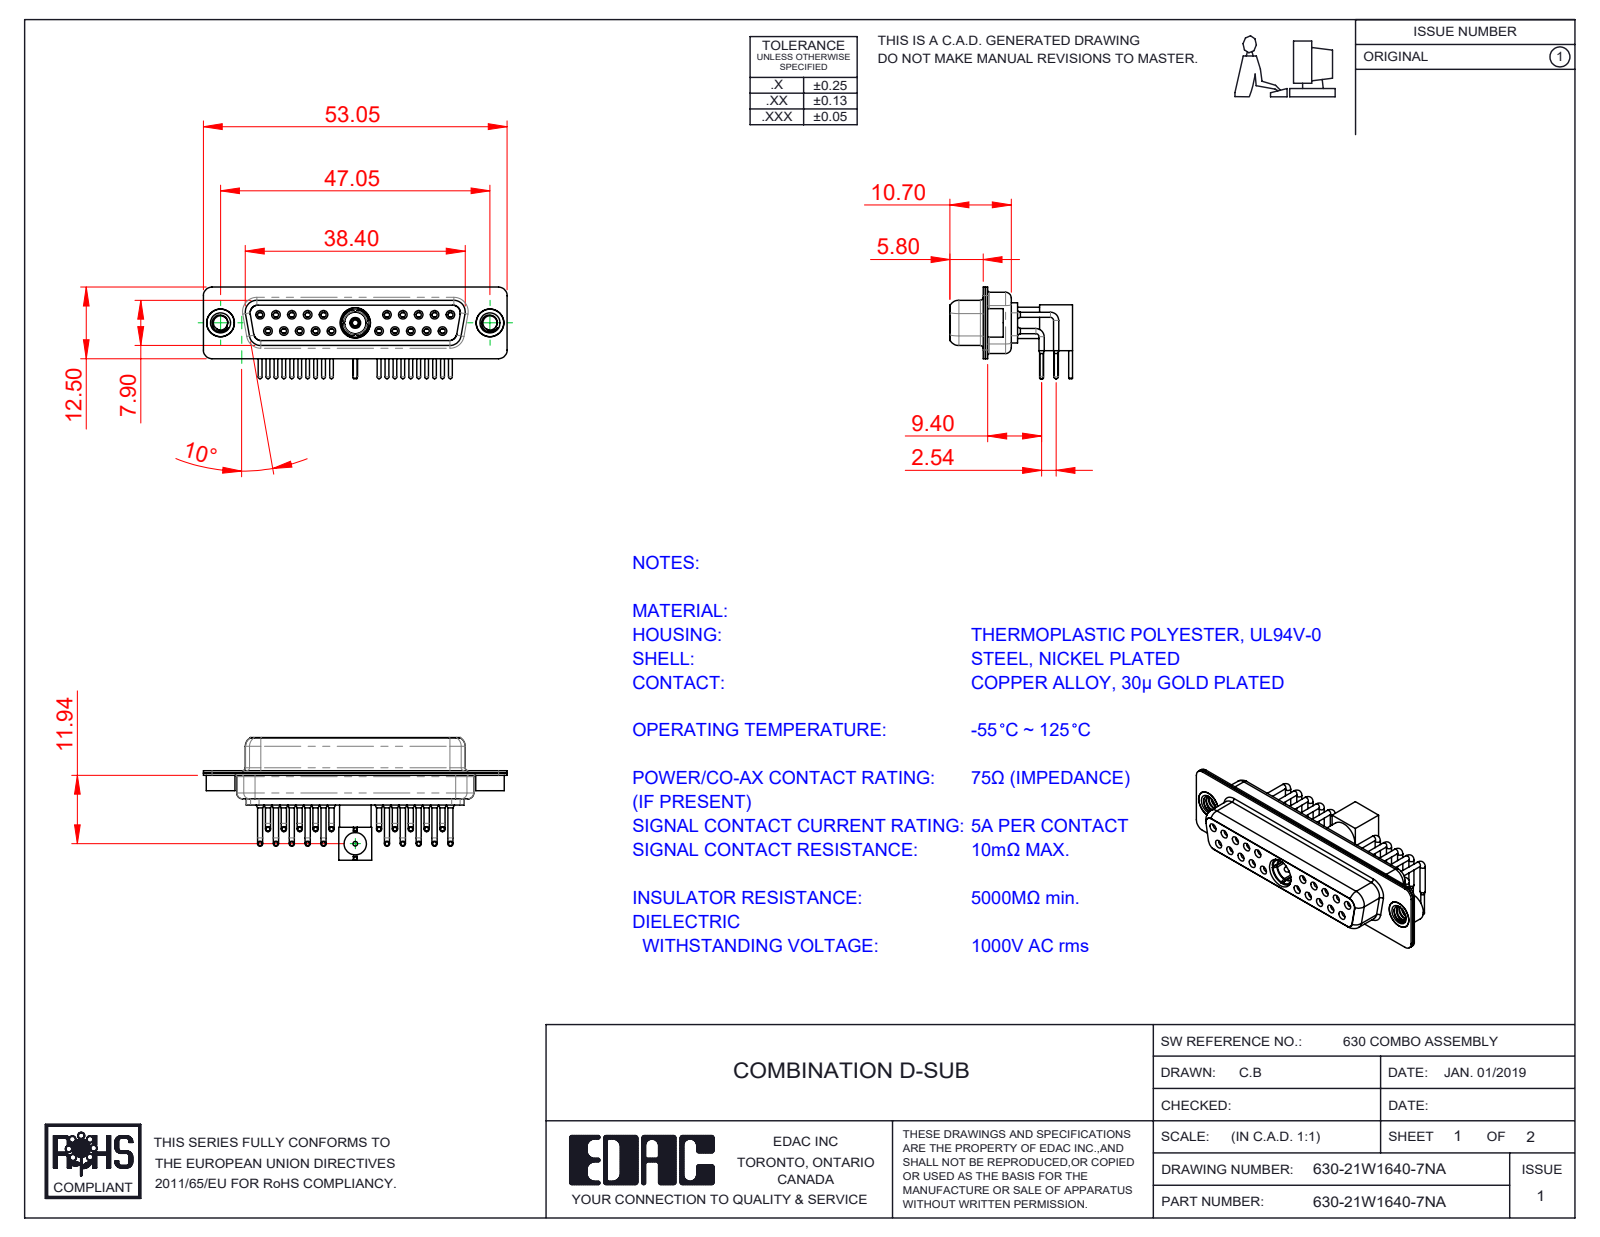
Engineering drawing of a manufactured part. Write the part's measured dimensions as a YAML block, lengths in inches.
part_name: "Insulator Pin_Straight PC Tail; Insulator RA Pin; 630Combo Shell Rear_25 Contacts; 630-21W1640-7NA (+8 more)"
step_written_by: "SolidWorks 2020 (CONFIG_CONTROL_DESIGN)"
units: inches
bodies: {solids: 31, faces: 1501, planar: 434, cylindrical: 660, other: 407}
overall_size: [2.089, 0.843, 0.63]
volume: 0.255
surface_area: 15.46
round_holes:
  - {diameter: 0.043, count: 21}
  - {diameter: 0.059, count: 21}
  - {diameter: 0.035, count: 20}
  - {diameter: 0.079, count: 20}
  - {diameter: 0.063, count: 10}
  - {diameter: 0.067, count: 10}
  - {diameter: 0.191, count: 3}
  - {diameter: 0.098, count: 2}
  - {diameter: 0.157, count: 2}
  - {diameter: 0.159, count: 2}
  - {diameter: 0.031, count: 1}
  - {diameter: 0.111, count: 1}
round_bosses_or_shafts:
  - {diameter: 0.035, count: 20}
  - {diameter: 0.026, count: 20}
  - {diameter: 0.063, count: 10}
  - {diameter: 0.197, count: 3}
  - {diameter: 0.195, count: 2}
  - {diameter: 0.189, count: 2}
  - {diameter: 0.217, count: 1}
  - {diameter: 0.205, count: 1}
partial_cylinders:
  - {radius: 0.059, count: 16}
  - {radius: 0.079, count: 12}
  - {radius: 0.053, count: 8}
  - {radius: 0.063, count: 8}
  - {radius: 0.01, count: 4}
  - {radius: 0.02, count: 4}
  - {radius: 0.024, count: 4}
  - {radius: 0.026, count: 4}
face_to_face_distances: [0.016, 0.055, 0.018, 0.333, 0.071, 0.35, 0.244, 0.278, 0.073, 0.031]
hole_center_spacings: [0.124, 0.109, 0.218, 0.327, 0.198, 0.763, 0.826, 0.872]
